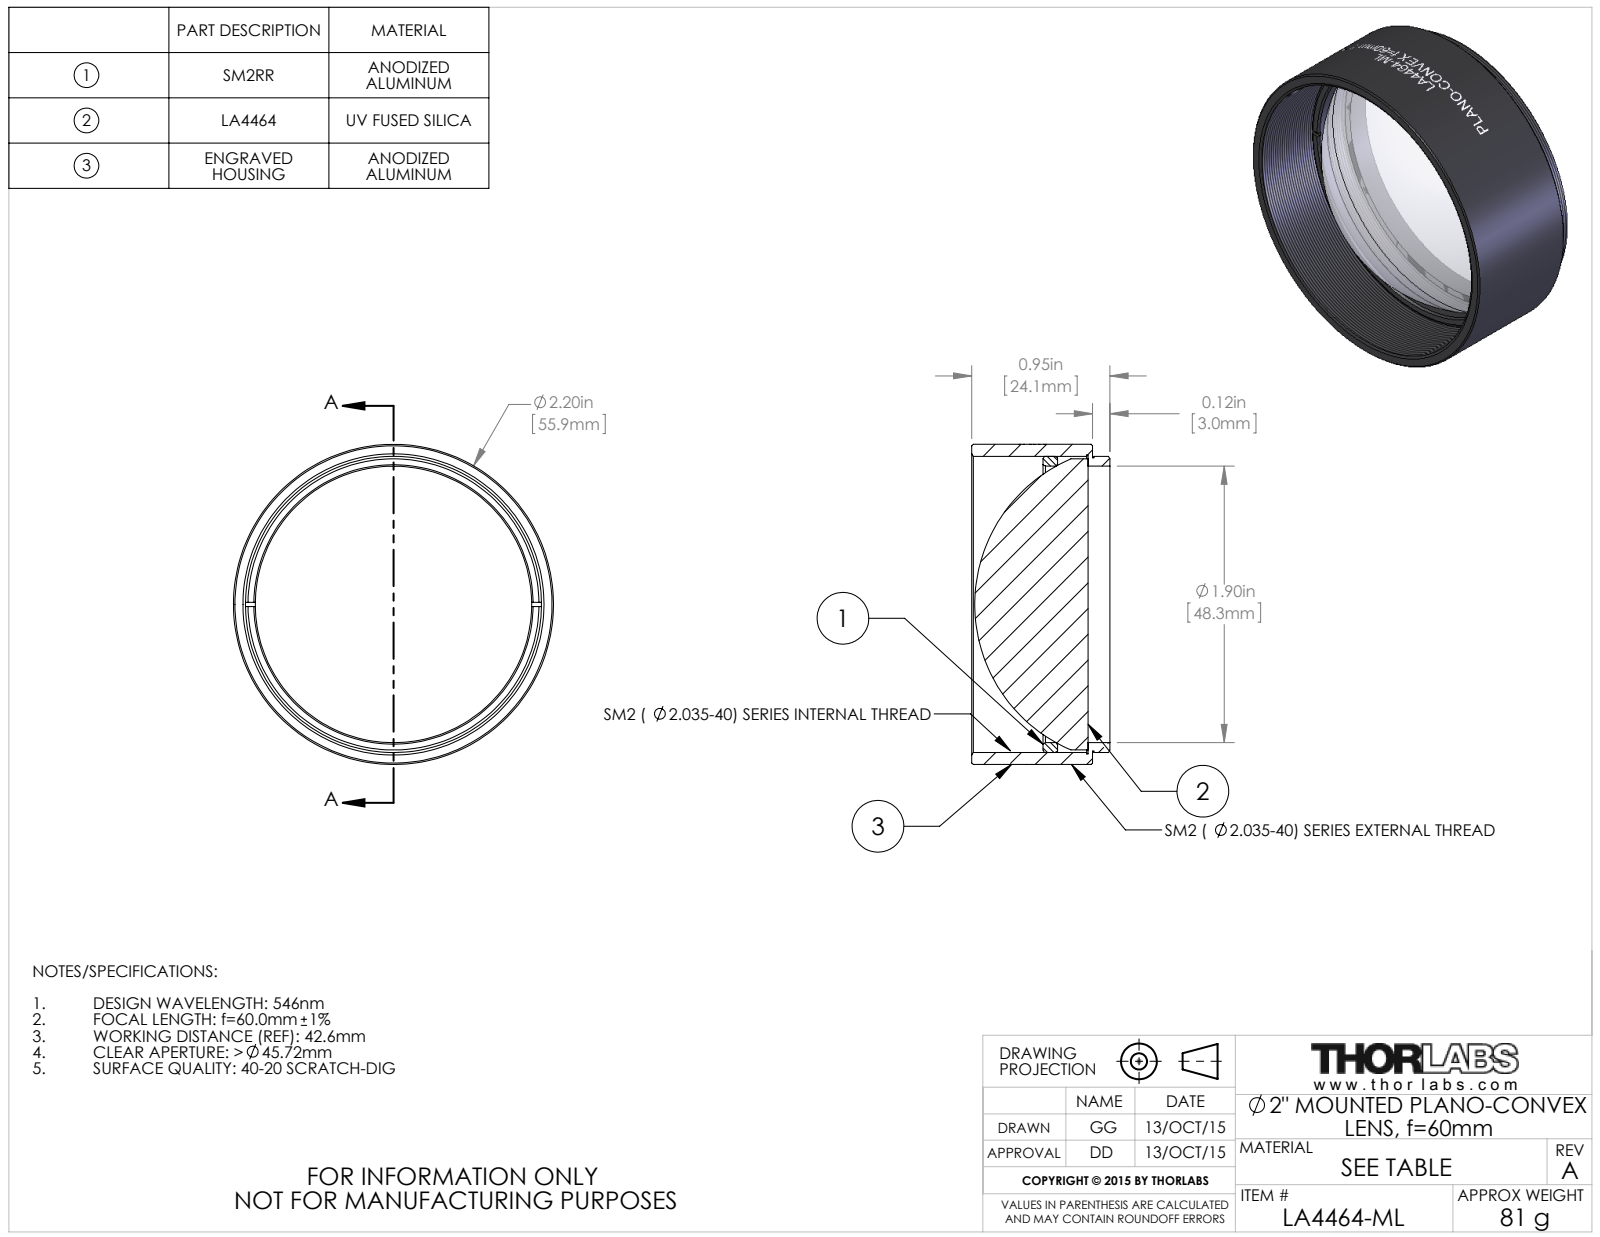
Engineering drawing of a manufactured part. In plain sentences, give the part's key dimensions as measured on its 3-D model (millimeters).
The part is named "TTN039283-E0W". Its 3-D file was written by "SolidWorks 2014 (CONFIG_CONTROL_DESIGN)". It is 3 solids with 110 faces: 16 planar, 74 cylindrical and 20 other. Overall it measures 55.9 by 55.9 by 24.1 millimeters. Its volume is 34 680 cubic millimeters and its surface area 16 010 square millimeters. Round holes: 1 of diameter 48.3, 1 of diameter 52.2. Round bosses or shafts: 1 of diameter 55.9, 1 of diameter 51.7, 1 of diameter 51.2, 1 of diameter 50.8. The main face-to-face distances are 0.8, 21.1, 20.3, 3, 3.8, 24.1, 9.1, 6.1, 5.4, 15.
